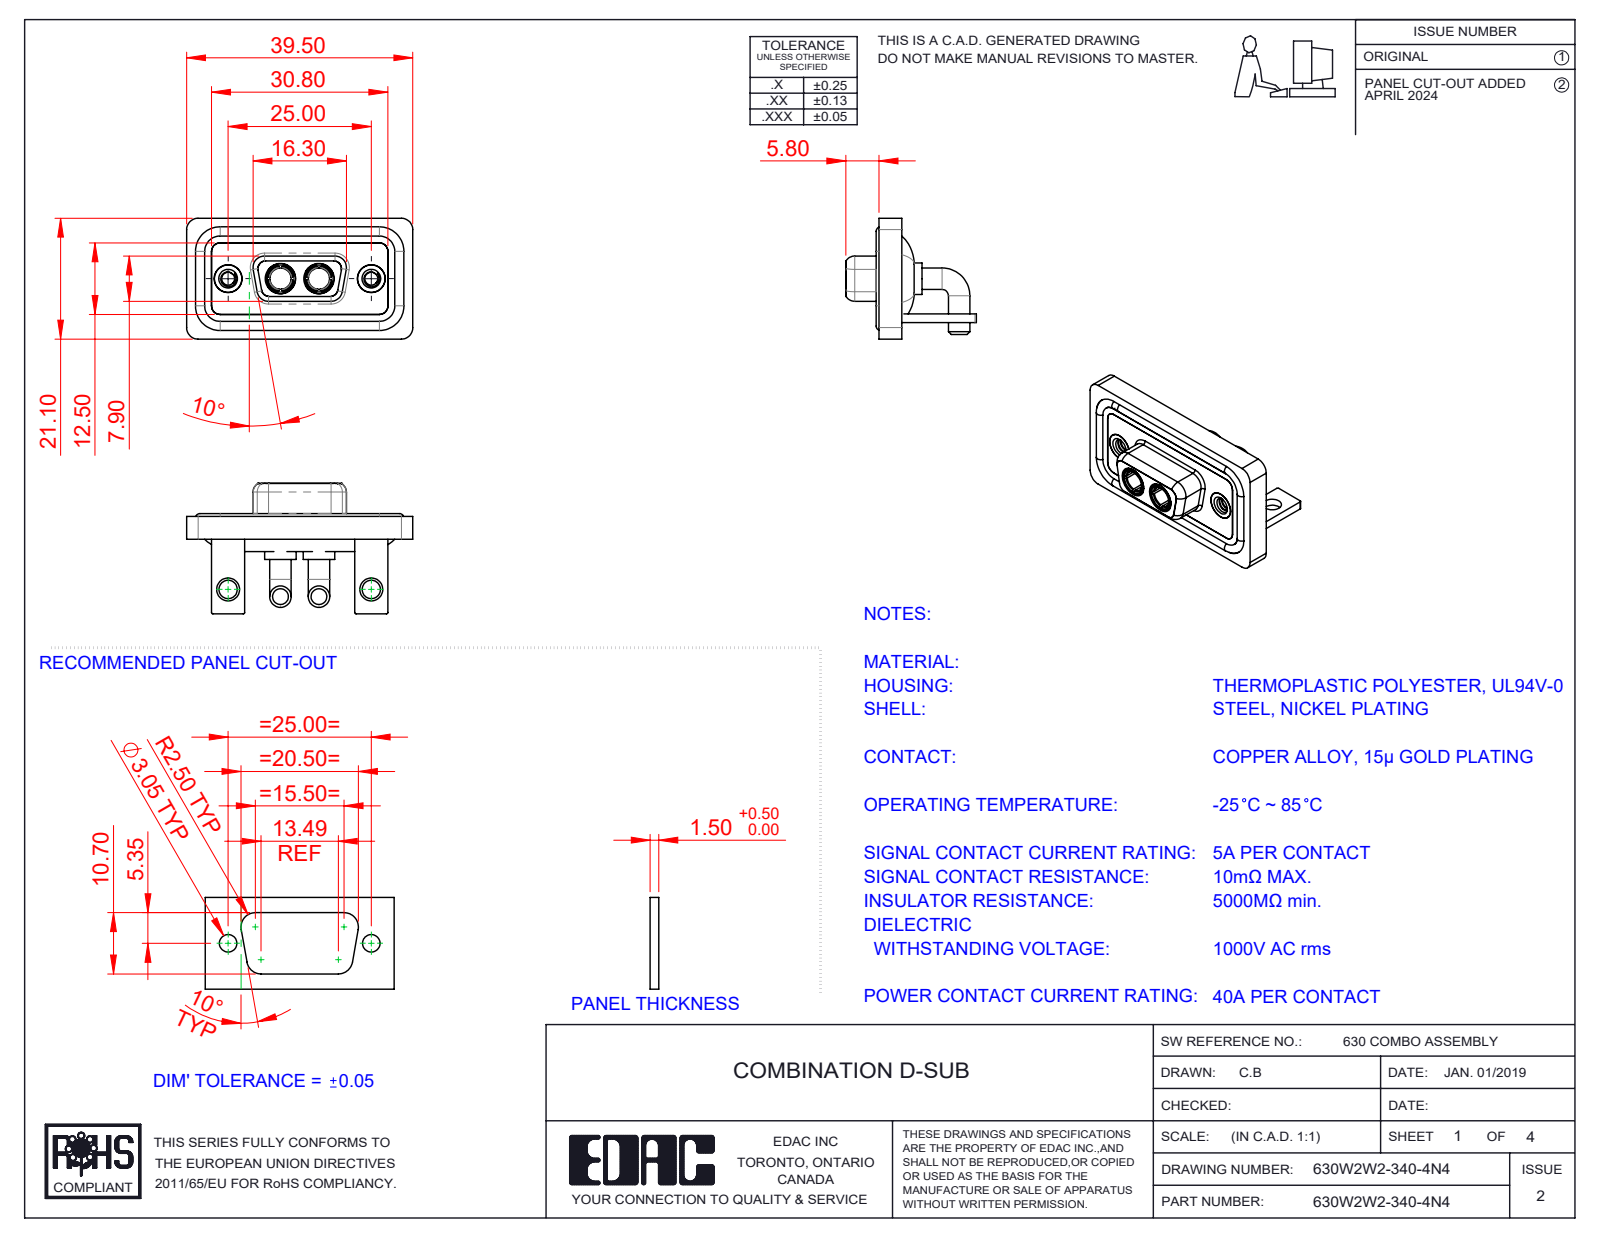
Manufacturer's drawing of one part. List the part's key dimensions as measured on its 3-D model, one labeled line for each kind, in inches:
Part name (STEP PRODUCT): 630Combo Housing_2W2; 630Combo Stabilizer Bracket_50 Contacts; 630Combo Waterproof Housing_09 Contacts; 630Combo Shell Rear_09 Contacts (+4 more)
STEP written by: SolidWorks 2023 (CONFIG_CONTROL_DESIGN)
Units: inches
Bodies: 13 solids, 590 faces (183 planar, 262 cylindrical, 145 other)
Overall size (bounding box): 1.555 × 0.898 × 0.831
Volume: 0.325 in³ · Surface area: 13.34 in²
Round holes (diameter × count): ⌀0.191 ×4, ⌀0.089 ×2, ⌀0.126 ×2, ⌀0.146 ×2, ⌀0.157 ×2, ⌀0.159 ×2, ⌀0.197 ×2, ⌀0.209 ×2
Round bosses / shafts (diameter × count): ⌀0.148 ×4, ⌀0.063 ×4, ⌀0.217 ×2, ⌀0.205 ×2, ⌀0.195 ×2, ⌀0.195 ×2, ⌀0.189 ×2, ⌀0.187 ×2
Partial cylindrical surfaces — rounded edges, fillets, slot ends (radius × count): R0.079 ×19, R0.059 ×18, R0.01 ×16, R0.053 ×8, R0.063 ×8, R0.02 ×5, R0.024 ×4, R0.026 ×4
Main face-to-face distances: 0.016, 0.114, 0.059, 0.071, 0.043, 0.146, 0.031, 0.098, 0.063, 0.122
Hole centre spacings: 0.36, 0.624, 0.984, 0.265
